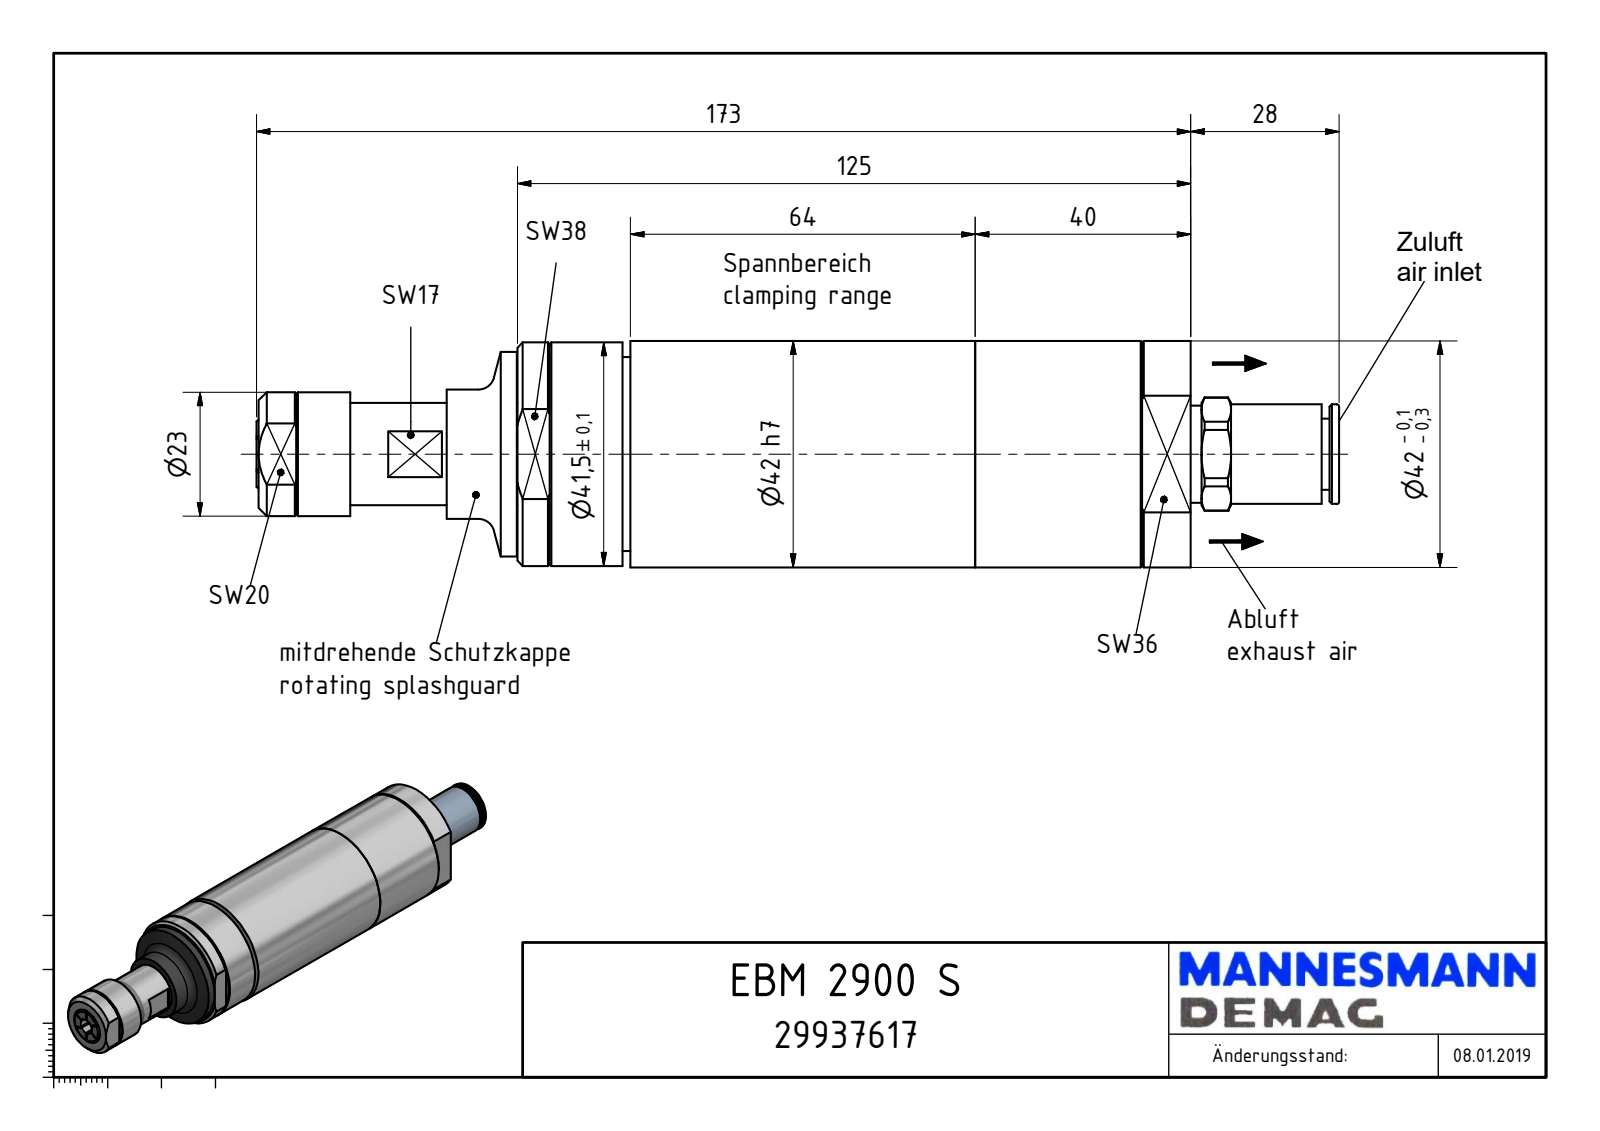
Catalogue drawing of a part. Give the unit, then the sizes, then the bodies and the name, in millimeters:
Units: millimetres
Overall size (bounding box): 200.97 × 42 × 42
Round holes (diameter × count): ⌀6 ×1, ⌀9.53 ×1, ⌀10.5 ×1, ⌀12 ×1, ⌀13.2 ×1, ⌀17.92 ×1, ⌀19.5 ×1
Round bosses / shafts (diameter × count): ⌀42 ×1, ⌀41.5 ×1, ⌀38 ×1, ⌀36 ×1, ⌀24 ×1, ⌀23 ×1, ⌀19 ×1, ⌀18.5 ×1
Partial cylindrical surfaces — rounded edges, fillets, slot ends (radius × count): R18.09 ×6, R33.72 ×6, R10.5 ×1
Main face-to-face distances: 0.5, 125, 1.5, 125.4, 0.4, 19.5, 9.75, 17.75, 18.25, 104
Volume: 193 522 mm³ · Surface area: 32 449 mm²
Bodies: 1 solid, 237 faces (112 planar, 57 cylindrical, 68 other)
Part name (STEP PRODUCT): EBM 2900 S_29937617
STEP written by: Autodesk Inventor 2018 (AUTOMOTIVE_DESIGN)
